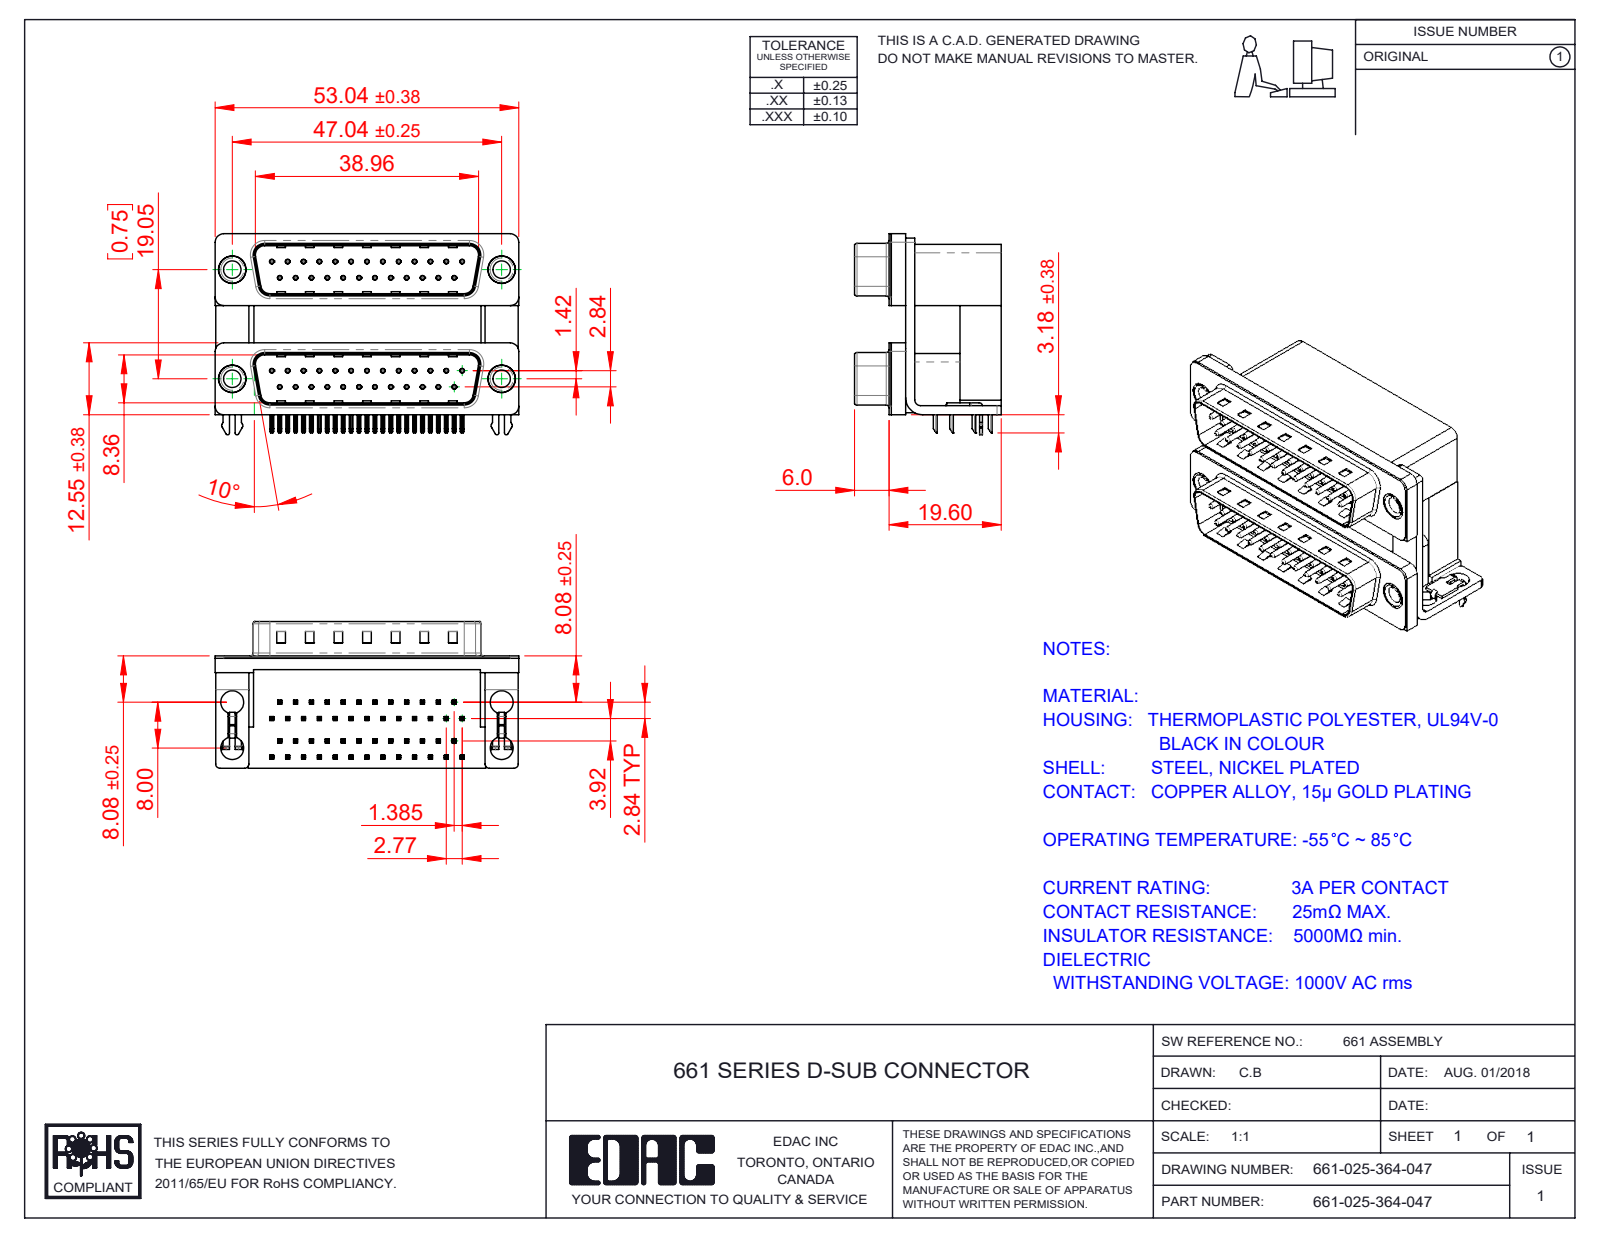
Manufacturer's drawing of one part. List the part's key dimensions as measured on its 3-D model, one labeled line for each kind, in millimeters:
Part name (STEP PRODUCT): 661 4 Prong Board Lock; 661 Contact Bottom Lower; 661 Contact Bottom Upper_M; 661 Housing Spacer_25 Contacts M (+8 more)
STEP written by: SolidWorks 2020 (CONFIG_CONTROL_DESIGN)
Units: millimetres
Bodies: 65 solids, 4722 faces (3034 planar, 1310 cylindrical, 378 other)
Overall size (bounding box): 53.04 × 34.9 × 25.6
Volume: 21 266 mm³ · Surface area: 22 445 mm²
Round holes (diameter × count): ⌀0.35 ×50, ⌀0.8 ×50, ⌀2 ×4, ⌀2.5 ×4, ⌀3.05 ×4, ⌀3.2 ×4, ⌀3.5 ×4, ⌀4 ×4, ⌀4.8 ×4, ⌀5 ×4
Round bosses / shafts (diameter × count): ⌀0.75 ×50, ⌀4.9 ×4, ⌀4.75 ×4, ⌀4 ×4, ⌀3.85 ×4, ⌀3.4 ×4, ⌀3.3 ×4, ⌀2.9 ×4
Partial cylindrical surfaces — rounded edges, fillets, slot ends (radius × count): R0.25 ×200, R0.12 ×100, R0.5 ×16, R1.5 ×14, R0.75 ×8, R0.9 ×8, R1.6 ×8, R2 ×8
Main face-to-face distances: 0.4, 19.2, 19.05, 7.2, 12, 10.69, 16.7, 9.5, 2.5, 8.36
Hole centre spacings: 3.16, 2.77, 5.54, 8.31, 11.08, 13.85, 16.62, 5.03
